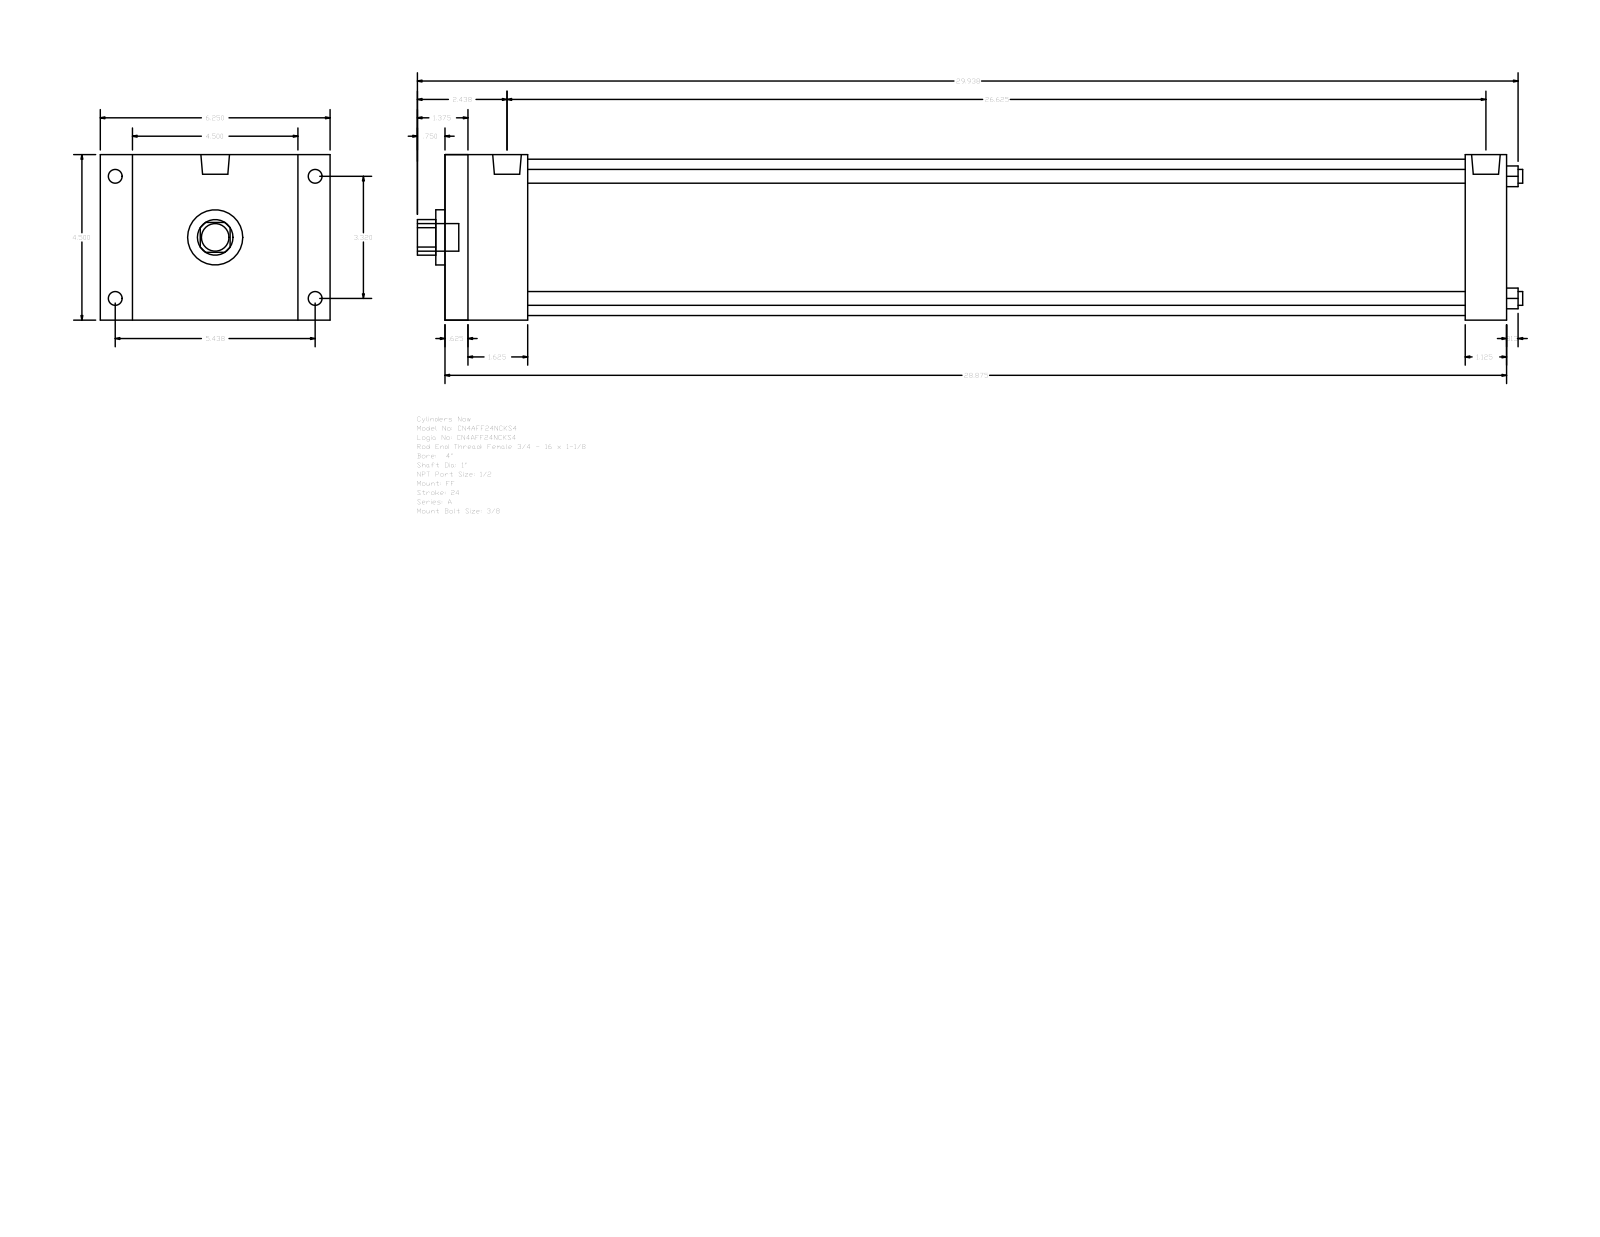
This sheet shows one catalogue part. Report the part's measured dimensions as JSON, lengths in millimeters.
{"part_name": "A_FF__0400_1", "step_written_by": "GSSL Pune (CONFIG_CONTROL_DESIGN)", "units": "millimeters", "bodies": {"solids": 0, "faces": 92, "planar": 64, "cylindrical": 28, "other": 0}, "overall_size": [763.59, 158.75, 114.3], "round_holes": [[9.53, 4], [25.4, 1], [38.1, 1], [107.95, 1]], "round_bosses_or_shafts": [[9.53, 4], [8.73, 4], [19.77, 2], [19.05, 1]], "partial_cylinders_radius": [[12.29, 1]], "face_to_face_distances": [114.3, 733.43, 15.87, 717.56, 22.23, 136.53, 704.85, 688.98, 28.58, 57.15], "hole_center_spacings": [59.62, 84.32, 119.25]}
